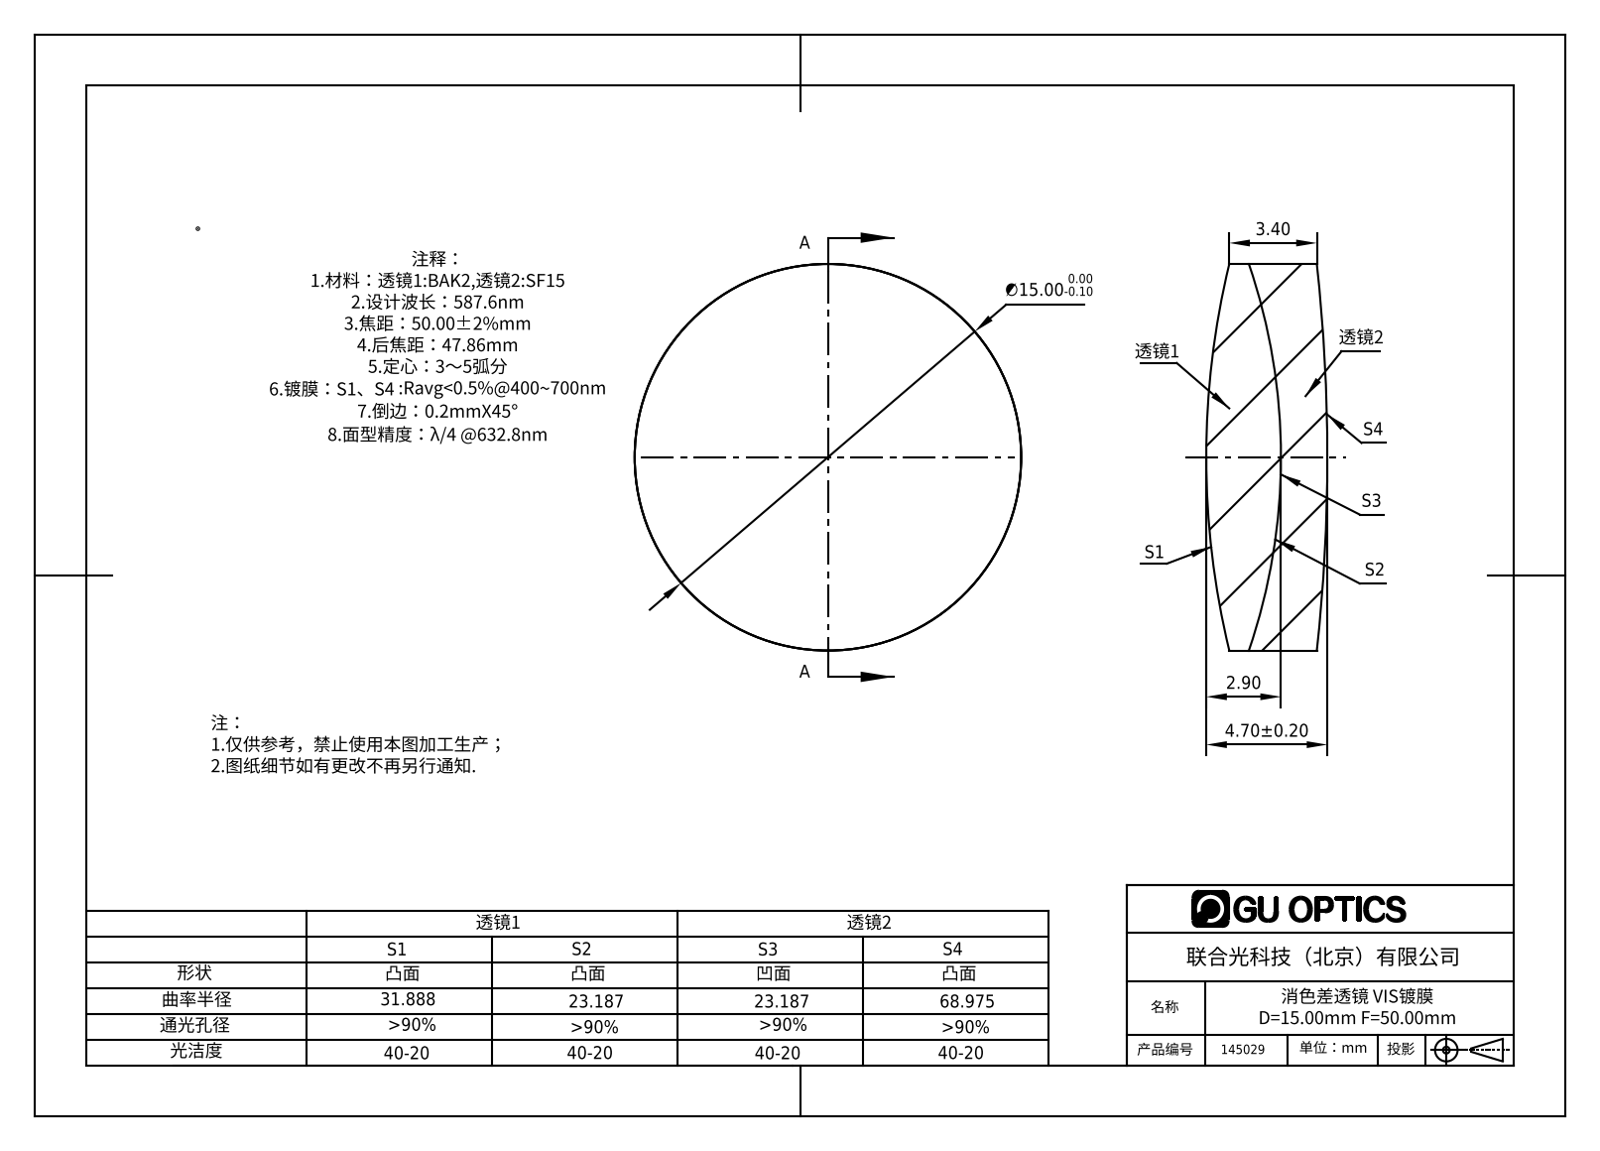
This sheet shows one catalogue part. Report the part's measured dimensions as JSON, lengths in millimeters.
{"part_name": "145029", "step_written_by": "SolidWorks 2016 (AUTOMOTIVE_DESIGN)", "units": "millimeters", "bodies": {"solids": 2, "faces": 12, "planar": 0, "cylindrical": 4, "other": 8}, "overall_size": [15, 15, 4.7], "volume_mm3": 716, "surface_area_mm2": 880, "round_bosses_or_shafts": [[15, 1]]}
